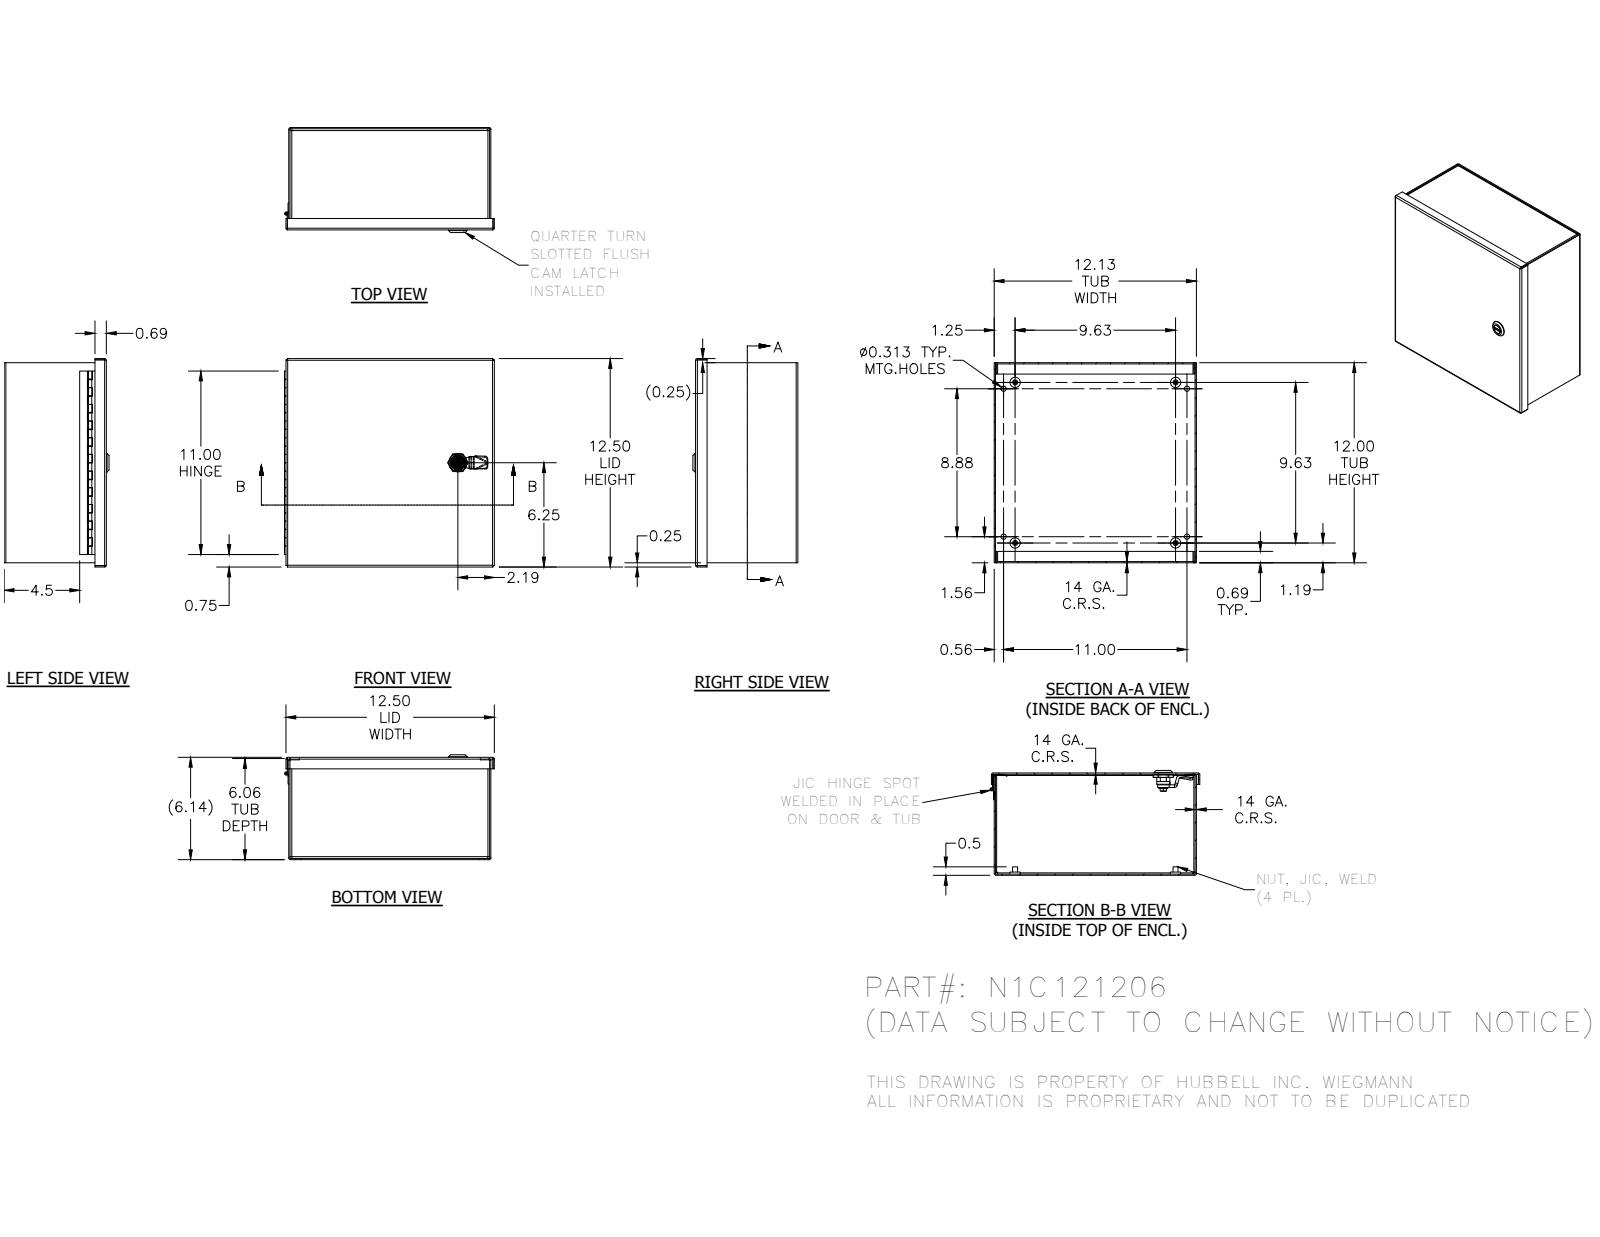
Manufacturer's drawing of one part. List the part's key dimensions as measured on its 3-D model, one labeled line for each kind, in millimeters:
Part name (STEP PRODUCT): N1C_SMALL; N1C1206TB; N1C121206BLR; HFW3513 (+8 more)
STEP written by: Autodesk Inventor 2012 (AUTOMOTIVE_DESIGN)
Units: millimetres
Bodies: 19 solids, 715 faces (411 planar, 222 cylindrical, 82 other)
Overall size (bounding box): 319.6 × 317.5 × 159.9
Volume: 842 100 mm³ · Surface area: 916 100 mm²
Round holes (diameter × count): ⌀4 ×4, ⌀8 ×4, ⌀2.9 ×1, ⌀5 ×1, ⌀8 ×1, ⌀10 ×1, ⌀10.2 ×1, ⌀16.1 ×1, ⌀20.4 ×1
Round bosses / shafts (diameter × count): ⌀15.9 ×4, ⌀7.6 ×4, ⌀28 ×1, ⌀22 ×1, ⌀19.8 ×1, ⌀16 ×1, ⌀15.2 ×1, ⌀13.5 ×1
Partial cylindrical surfaces — rounded edges, fillets, slot ends (radius × count): R0.3 ×30, R0.8 ×16, R2.7 ×16, R0.5 ×10, R4 ×4, R0.4 ×3, R1 ×1, R4.4 ×1
Main face-to-face distances: 1.9, 154, 152.1, 306.1, 155.9, 302.9, 304.2, 308, 304.8, 301
Hole centre spacings: 19.9, 235.6, 244.5, 262.1, 351.9, 118.3, 123.6, 225.4
